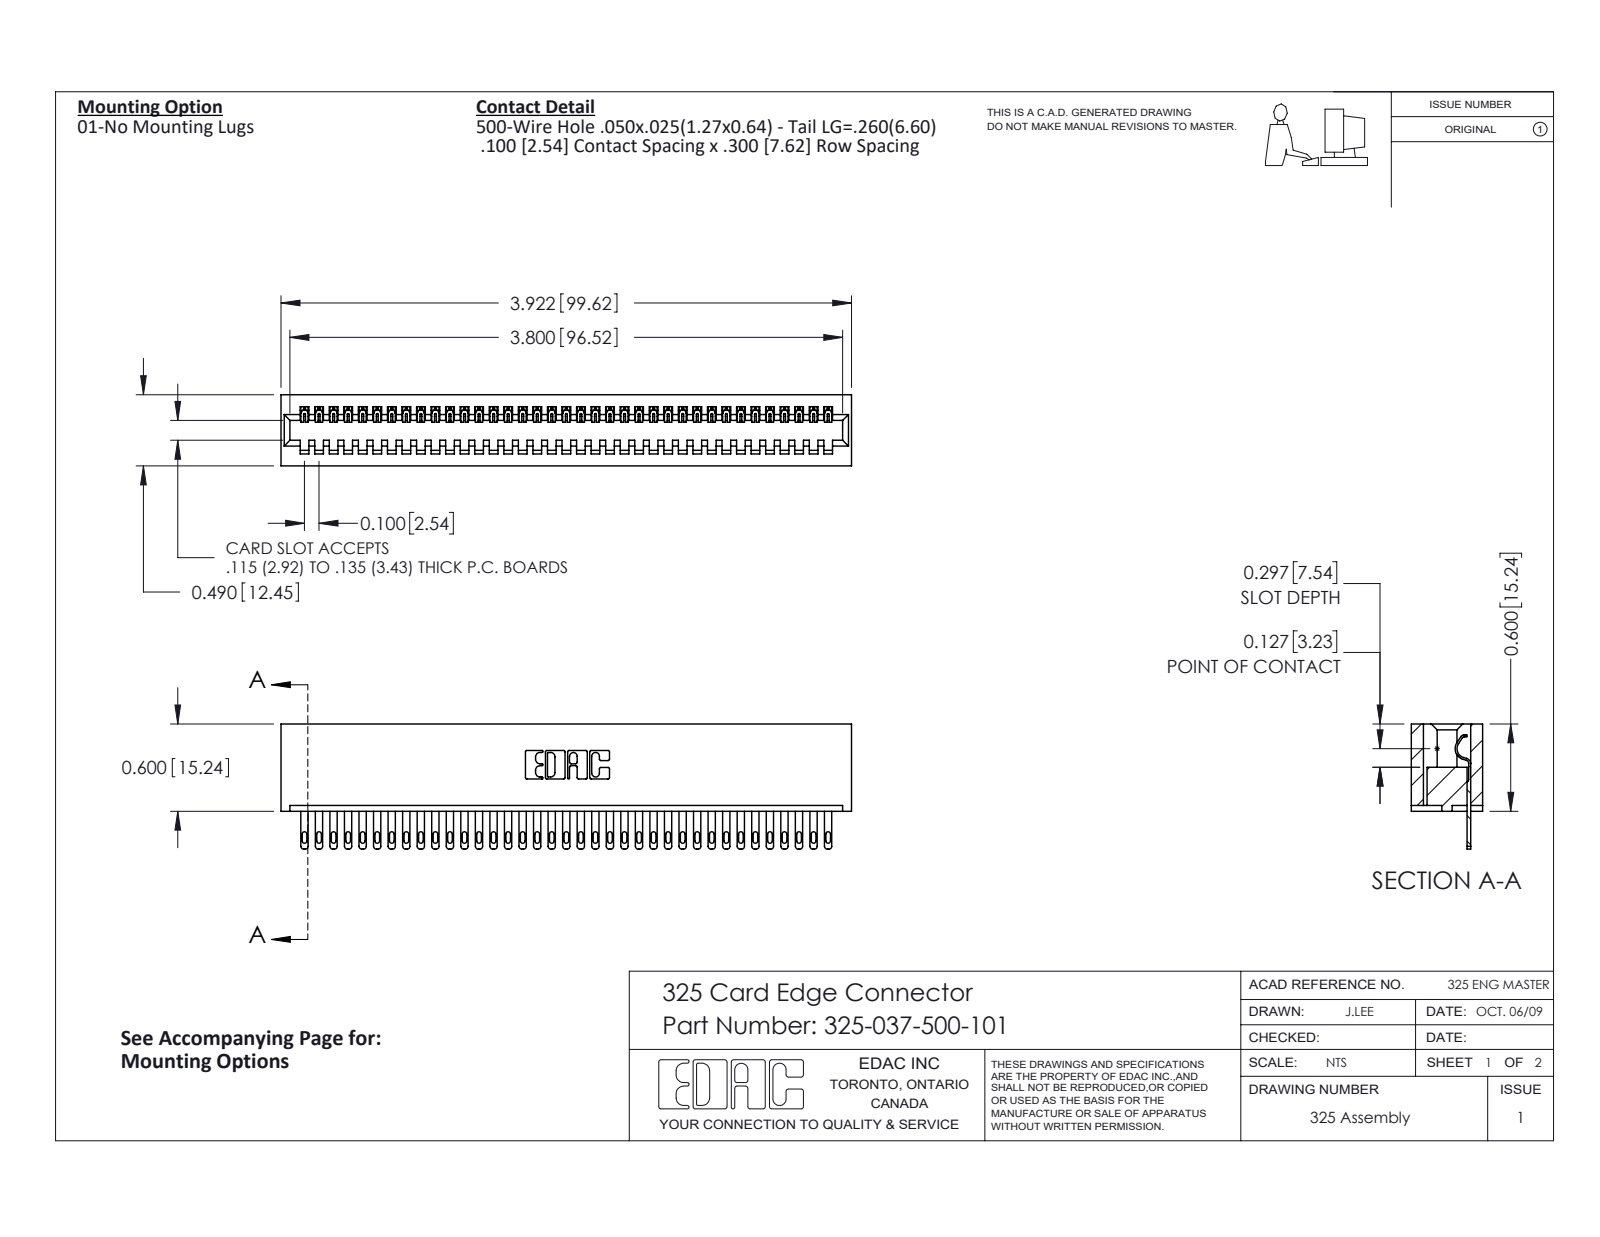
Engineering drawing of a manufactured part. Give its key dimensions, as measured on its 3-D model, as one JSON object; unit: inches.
{"part_name": "325 Part_Lugless; 325-292-001_325-293-100; 325-037-500-101", "step_written_by": "SolidWorks 2016 (CONFIG_CONTROL_DESIGN)", "units": "inches", "bodies": {"solids": 38, "faces": 2104, "planar": 1398, "cylindrical": 706, "other": 0}, "overall_size": [3.922, 0.86, 0.49], "volume_in3": 0.806, "surface_area_in2": 23.12, "partial_cylinders_radius": [[0.006, 74], [0.016, 74], [0.02, 74], [0.01, 22], [0.007, 6], [0.031, 6], [0.026, 3], [0.014, 1]], "face_to_face_distances": [0.083, 0.407, 0.3, 0.49, 0.107, 0.383, 0.025, 0.325, 0.56, 0.263]}
